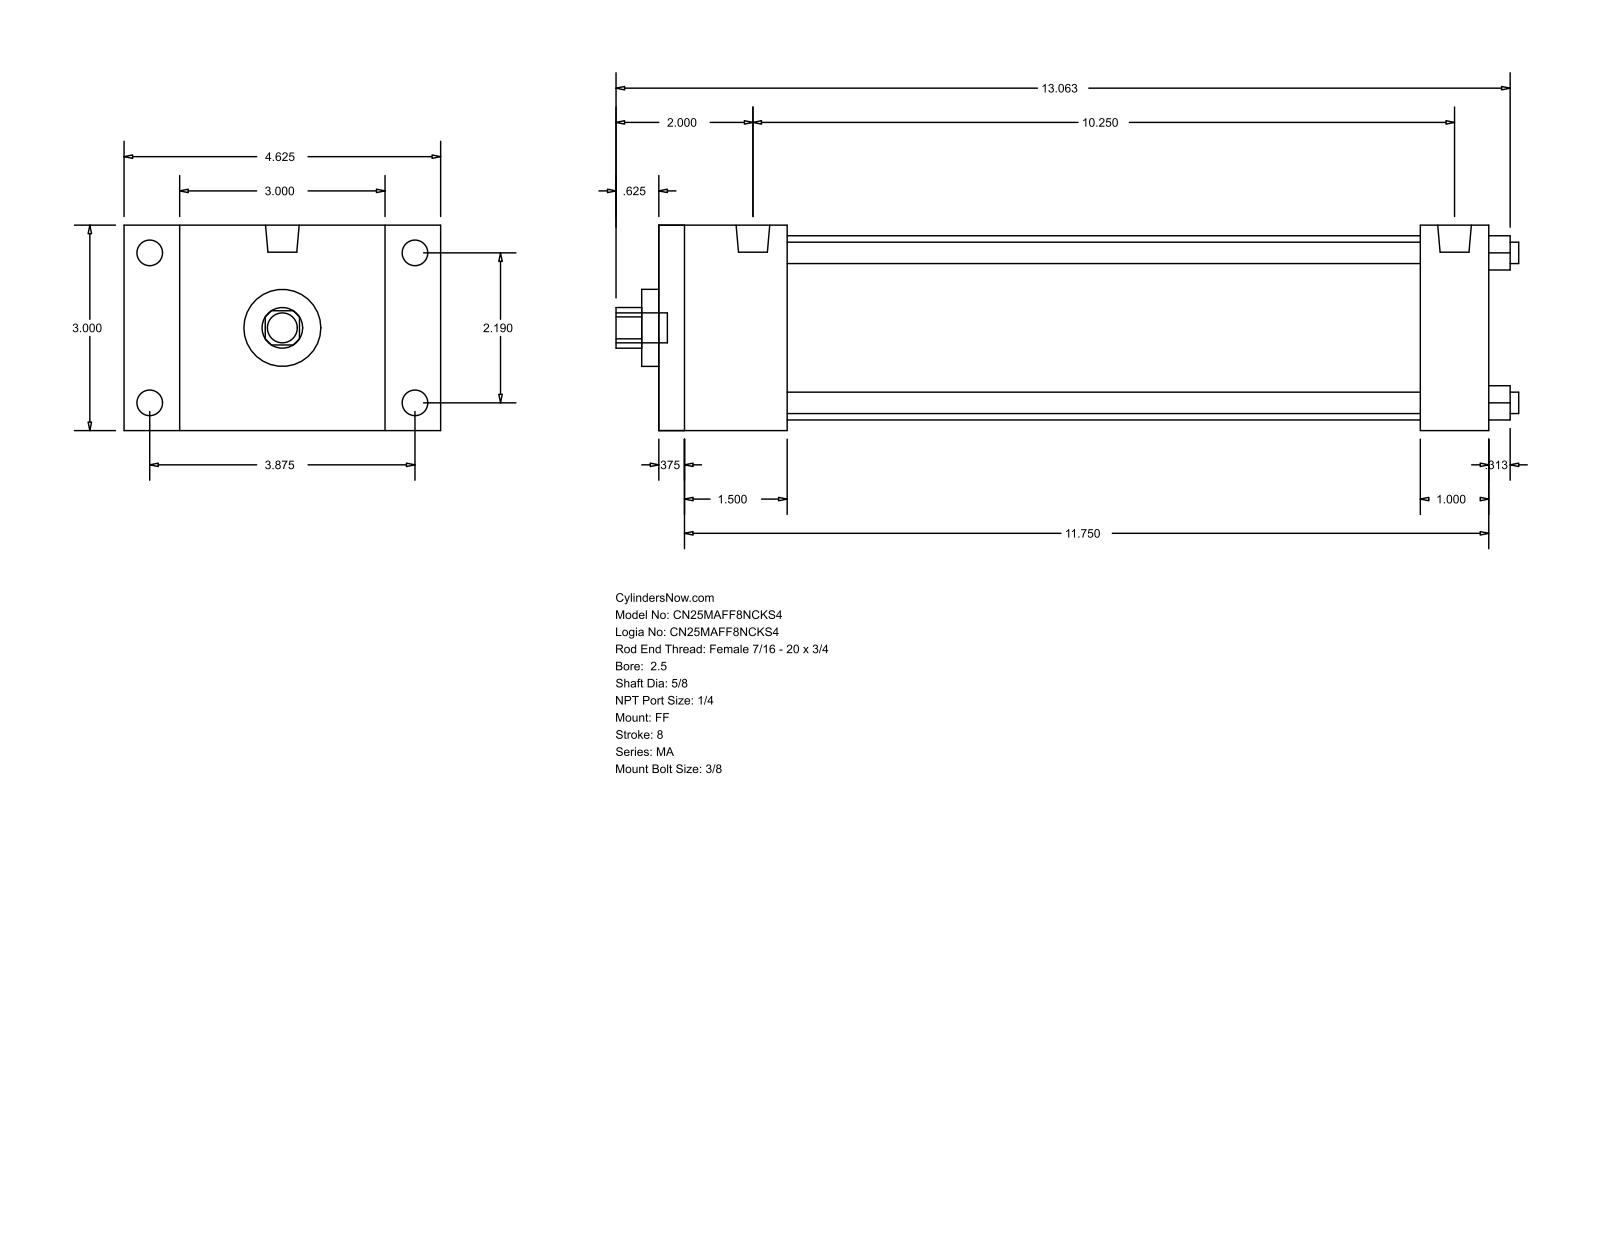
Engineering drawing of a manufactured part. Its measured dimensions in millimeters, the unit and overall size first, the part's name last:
Units: millimetres
Overall size (bounding box): 334.96 × 117.47 × 76.2
Round holes (diameter × count): ⌀7.94 ×4, ⌀15.88 ×1, ⌀28.57 ×1, ⌀68.33 ×1
Round bosses / shafts (diameter × count): ⌀9.53 ×4, ⌀7.94 ×4, ⌀12.49 ×2, ⌀11.11 ×1
Partial cylindrical surfaces — rounded edges, fillets, slot ends (radius × count): R7.54 ×1
Main face-to-face distances: 76.2, 307.97, 9.52, 298.45, 25.4, 47.62, 282.57, 38.1, 273.05, 234.95
Hole centre spacings: 39.33, 55.62, 78.66
Bodies: 0 solids, 92 faces (64 planar, 28 cylindrical, 0 other)
Part name (STEP PRODUCT): MA_FF__0250_0.625
STEP written by: GSSL Pune (CONFIG_CONTROL_DESIGN)
